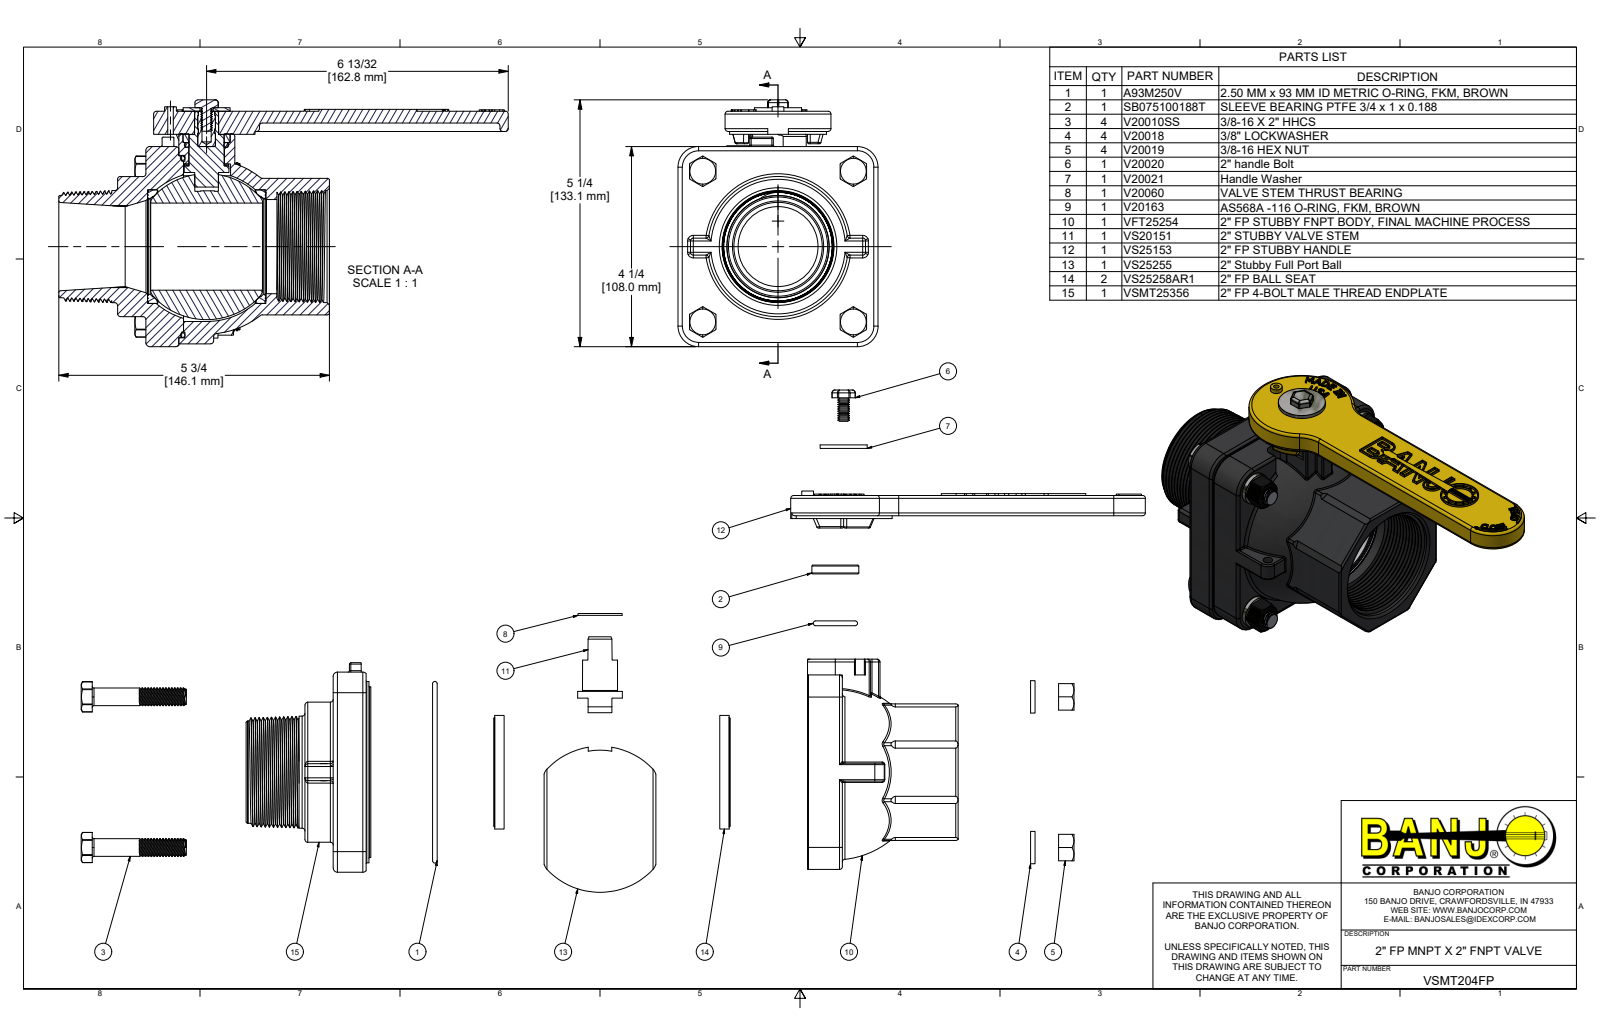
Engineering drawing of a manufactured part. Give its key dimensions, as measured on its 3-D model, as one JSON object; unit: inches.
{"part_name": "VSMT204FP; VFT25254; VFT25254Y; VFT25254X (+8 more)", "step_written_by": "Autodesk Inventor 2022 (AUTOMOTIVE_DESIGN)", "units": "inches", "bodies": {"solids": 26, "faces": 2046, "planar": 631, "cylindrical": 625, "other": 790}, "overall_size": [9.55, 5.242, 4.25], "volume_in3": 41.03, "surface_area_in2": 306.7, "round_holes": [[0.307, 4], [0.385, 4], [0.44, 4], [0.2, 2], [0.26, 2], [0.118, 1], [0.196, 1], [0.281, 1], [0.351, 1], [0.375, 1], [0.544, 1], [0.75, 1]], "round_bosses_or_shafts": [[0.324, 60], [0.687, 4], [0.375, 4], [3.85, 1], [3.625, 1], [2.975, 1], [2.412, 1], [2.38, 1]], "partial_cylinders_radius": [[0.06, 57], [0.03, 31], [0.09, 16], [0.162, 8], [0.32, 4], [0.468, 4], [0.015, 3], [0.2, 3]], "face_to_face_distances": [0.7, 0.06, 3.515, 0.615, 0.1, 0.8, 4.19, 1.44, 0.74, 0.64], "hole_center_spacings": [2.263, 3.2, 1.79, 2.041, 2.214, 2.341, 2.457, 4.202]}
